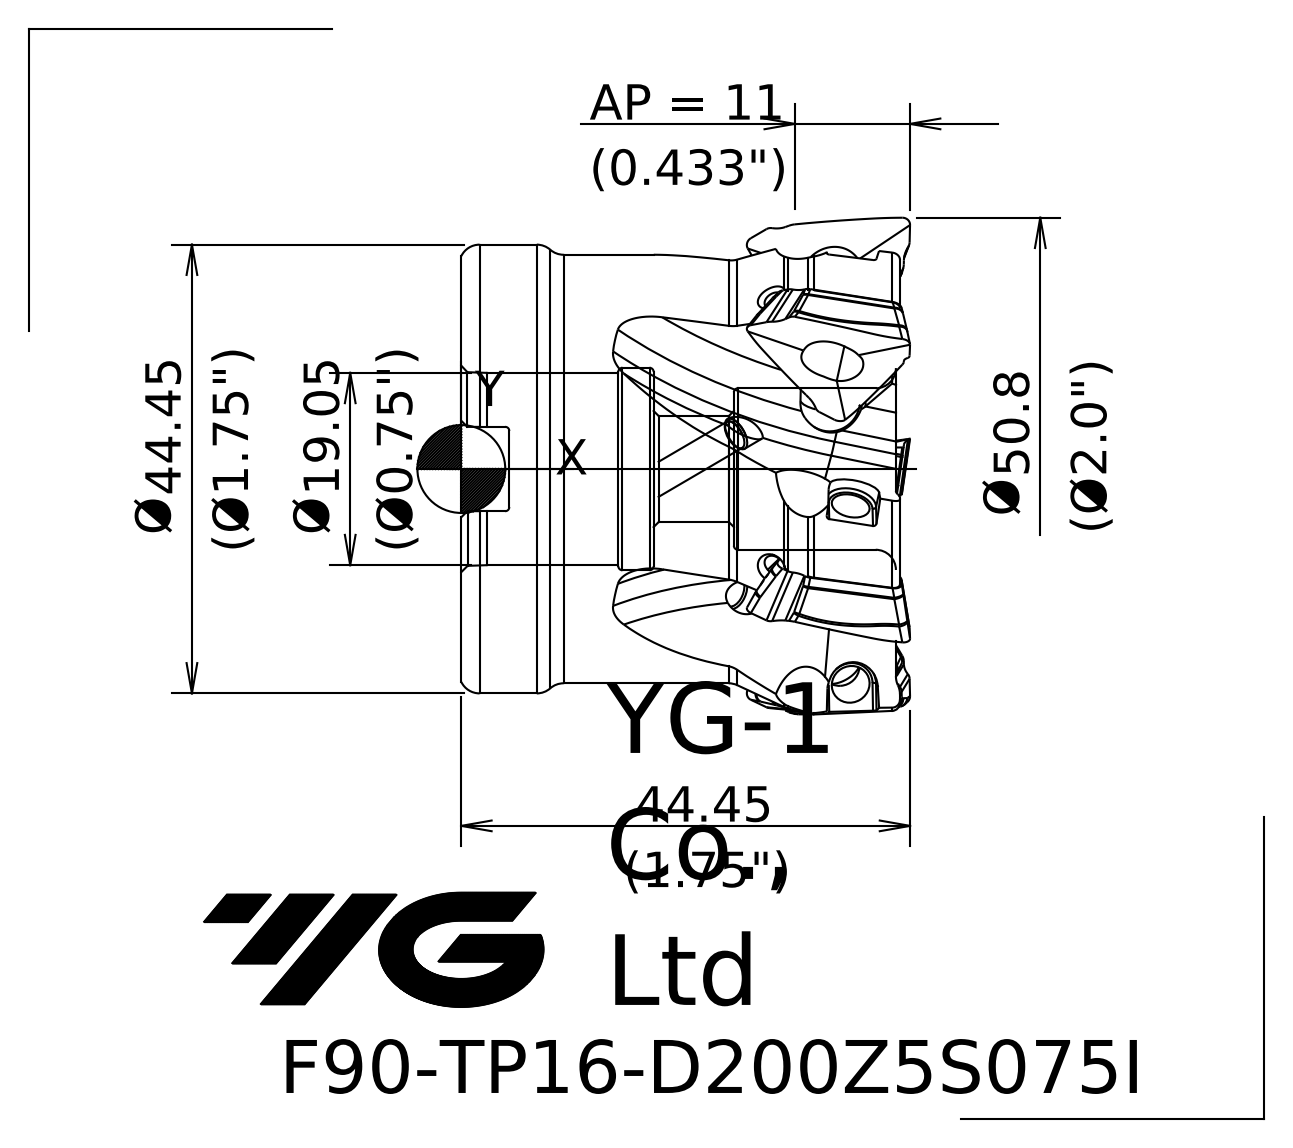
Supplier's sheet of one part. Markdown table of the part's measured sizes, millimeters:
| quantity | value |
| --- | --- |
| part name | 10223BFCFCF2pov0 |
| STEP written by | SIEMENS PLM Software NX 10.0 (AP203_CONFIGURATION_CONTROLLED_3D_DESIGN_OF_MECHANICAL_PARTS_AND_ASSEMBLIES_MIM_LF) |
| units | millimeters |
| bodies | 1 solid, 90 faces (17 planar, 20 cylindrical, 53 other) |
| overall size | 50.89 × 50.89 × 44.45 |
| volume | 55 847 mm³ |
| surface area | 18 946 mm² |
| round holes (diameter × count) | 3 × 5, 3.4 × 5, 10.5 × 1, 16 × 1, 19.05 × 1, 20.05 × 1 |
| round bosses / shafts (diameter × count) | 44.45 × 1, 42.45 × 1 |
| partial cylindrical surfaces (radius × count) | 0.4 × 2 |
| main face-to-face distances | 43.05, 38.3, 4.75, 24, 14.3, 19.05, 8.35, 16.05, 7.95, 22.25 |
